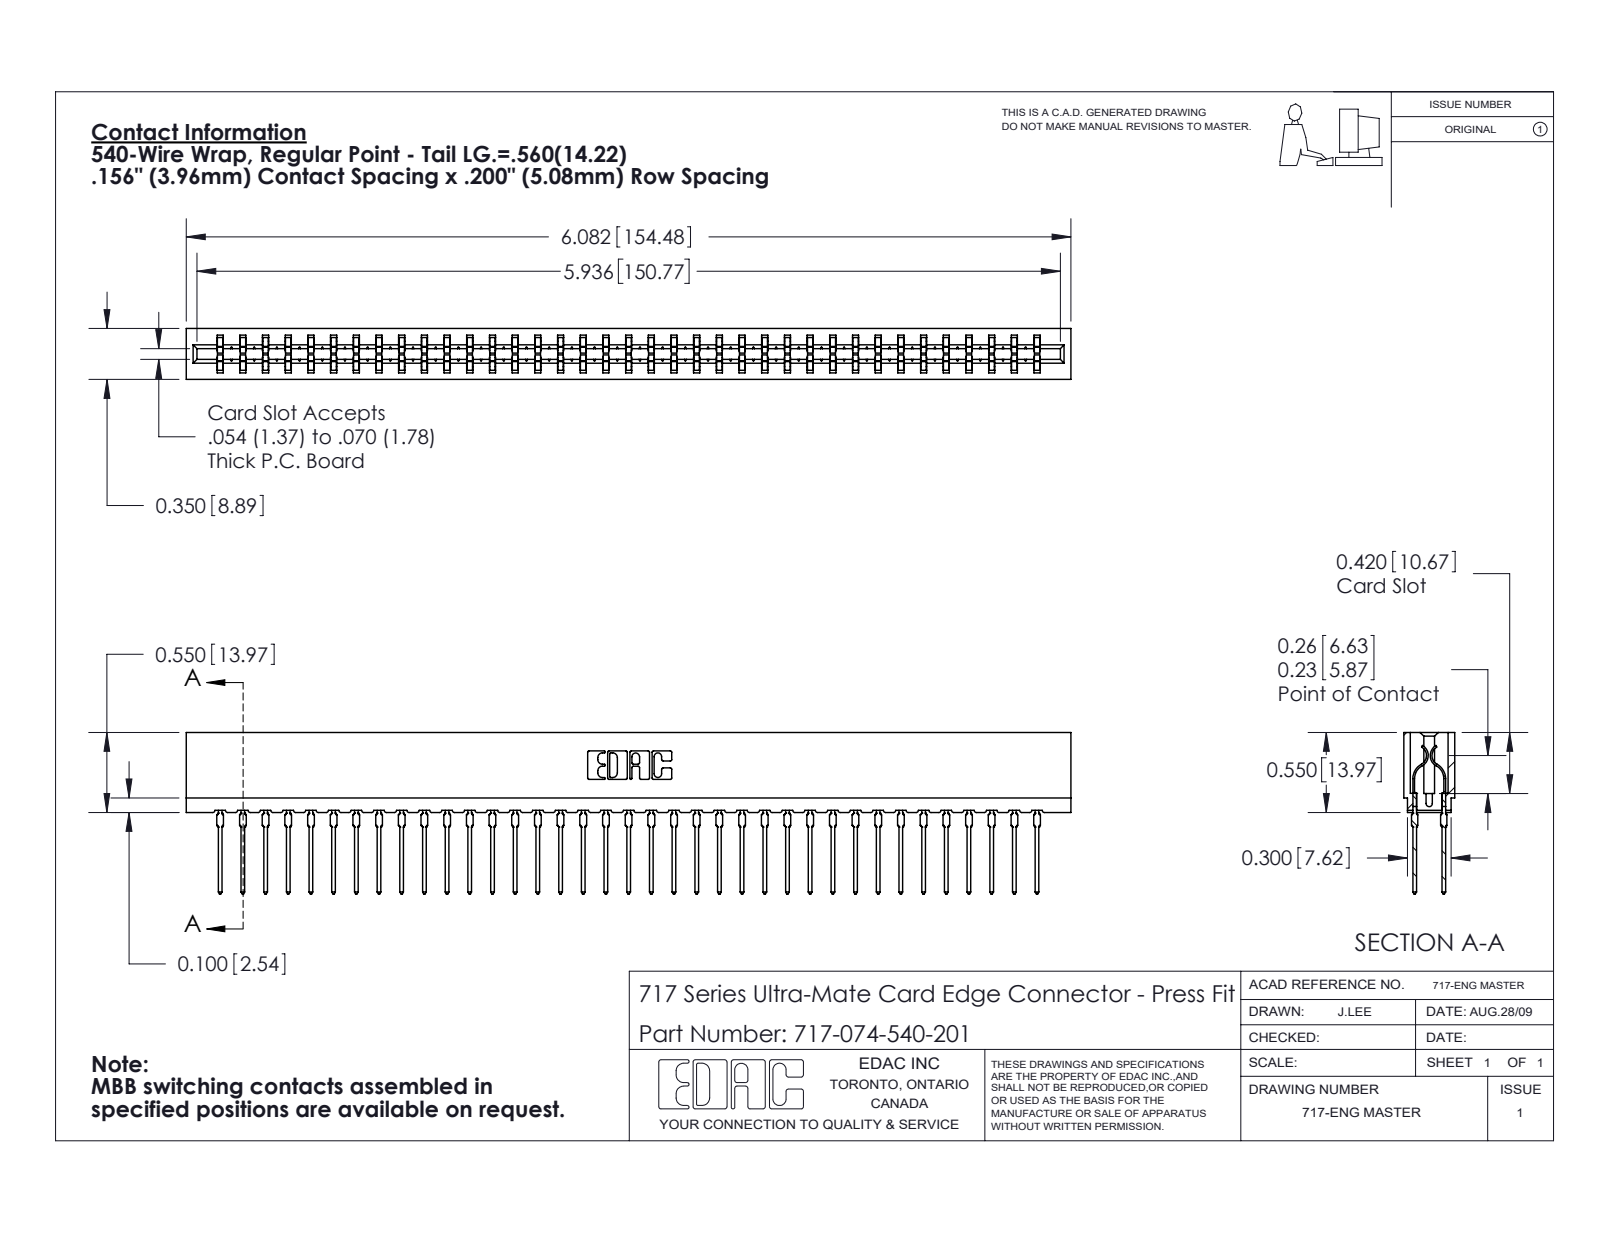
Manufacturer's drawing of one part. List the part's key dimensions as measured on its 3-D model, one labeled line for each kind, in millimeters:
Part name (STEP PRODUCT): 717 Part_Insulator Option - 06; 745-292-001_540; 717-074-540-201
STEP written by: SolidWorks 2020 (CONFIG_CONTROL_DESIGN)
Units: millimetres
Bodies: 75 solids, 6754 faces (3495 planar, 1335 cylindrical, 1924 other)
Overall size (bounding box): 154.5 × 28.2 × 8.9
Volume: 13 600 mm³ · Surface area: 21 740 mm²
Partial cylindrical surfaces — rounded edges, fillets, slot ends (radius × count): R0.5 ×148, R0.4 ×74, R0.3 ×22, R0.1 ×8, R0.3 ×8, R0.2 ×6, R0.8 ×6, R0.7 ×3
Main face-to-face distances: 5.4, 3.5, 8.9, 1.6, 7.3, 1.9, 3.8, 1.9, 2.2, 6.7
